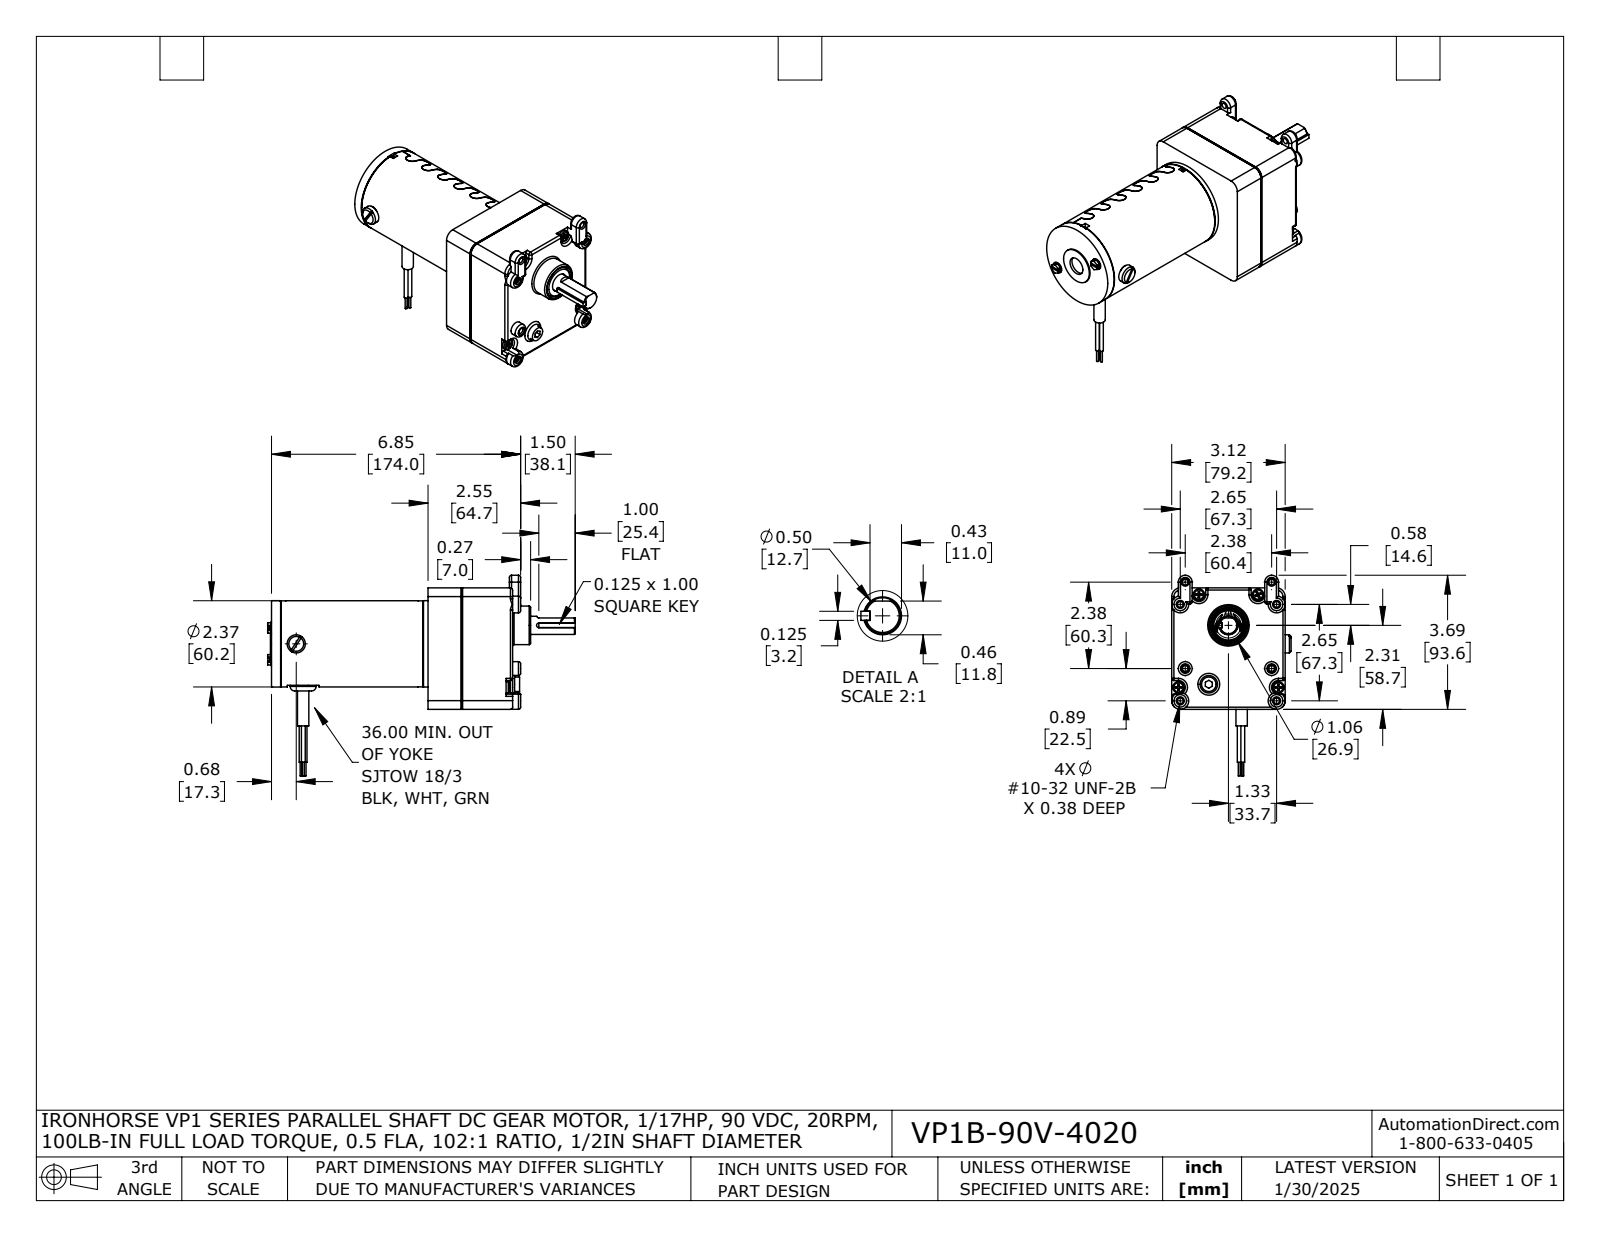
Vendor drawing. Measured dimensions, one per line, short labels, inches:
name: VP1B-90V-4020
written by: SolidWorks 2021 (AUTOMOTIVE_DESIGN)
unit: in
bodies: 20 solids, 910 faces (336 planar, 418 cylindrical, 156 other)
size: 8.457 × 5.516 × 3.283
volume: 11.85 in³; area: 218.1 in²
holes: 11× ⌀0.2, 8× ⌀0.158, 4× ⌀0.18, 2× ⌀0.187, 2× ⌀0.189, 2× ⌀0.22, 1× ⌀0.213, 1× ⌀0.336, 1× ⌀0.468, 1× ⌀0.5, 1× ⌀0.521, 1× ⌀0.688
bosses: 4× ⌀0.314, 4× ⌀0.313, 4× ⌀0.136, 3× ⌀0.105, 3× ⌀0.052, 2× ⌀0.5, 2× ⌀0.466, 2× ⌀0.44
rounds: 34× R0.06, 21× R0.062, 12× R0.156, 6× R0.15, 6× R0.151, 6× R0.161, 4× R0.12, 4× R0.235
face distances: 0.09, 3.12, 1.38, 2.326, 0.946, 0.106, 1.274, 2.22, 3.34, 0.315
hole spacings: 1.68, 2.65, 1.074, 2.729, 3.093, 0.077, 0.297, 0.373
